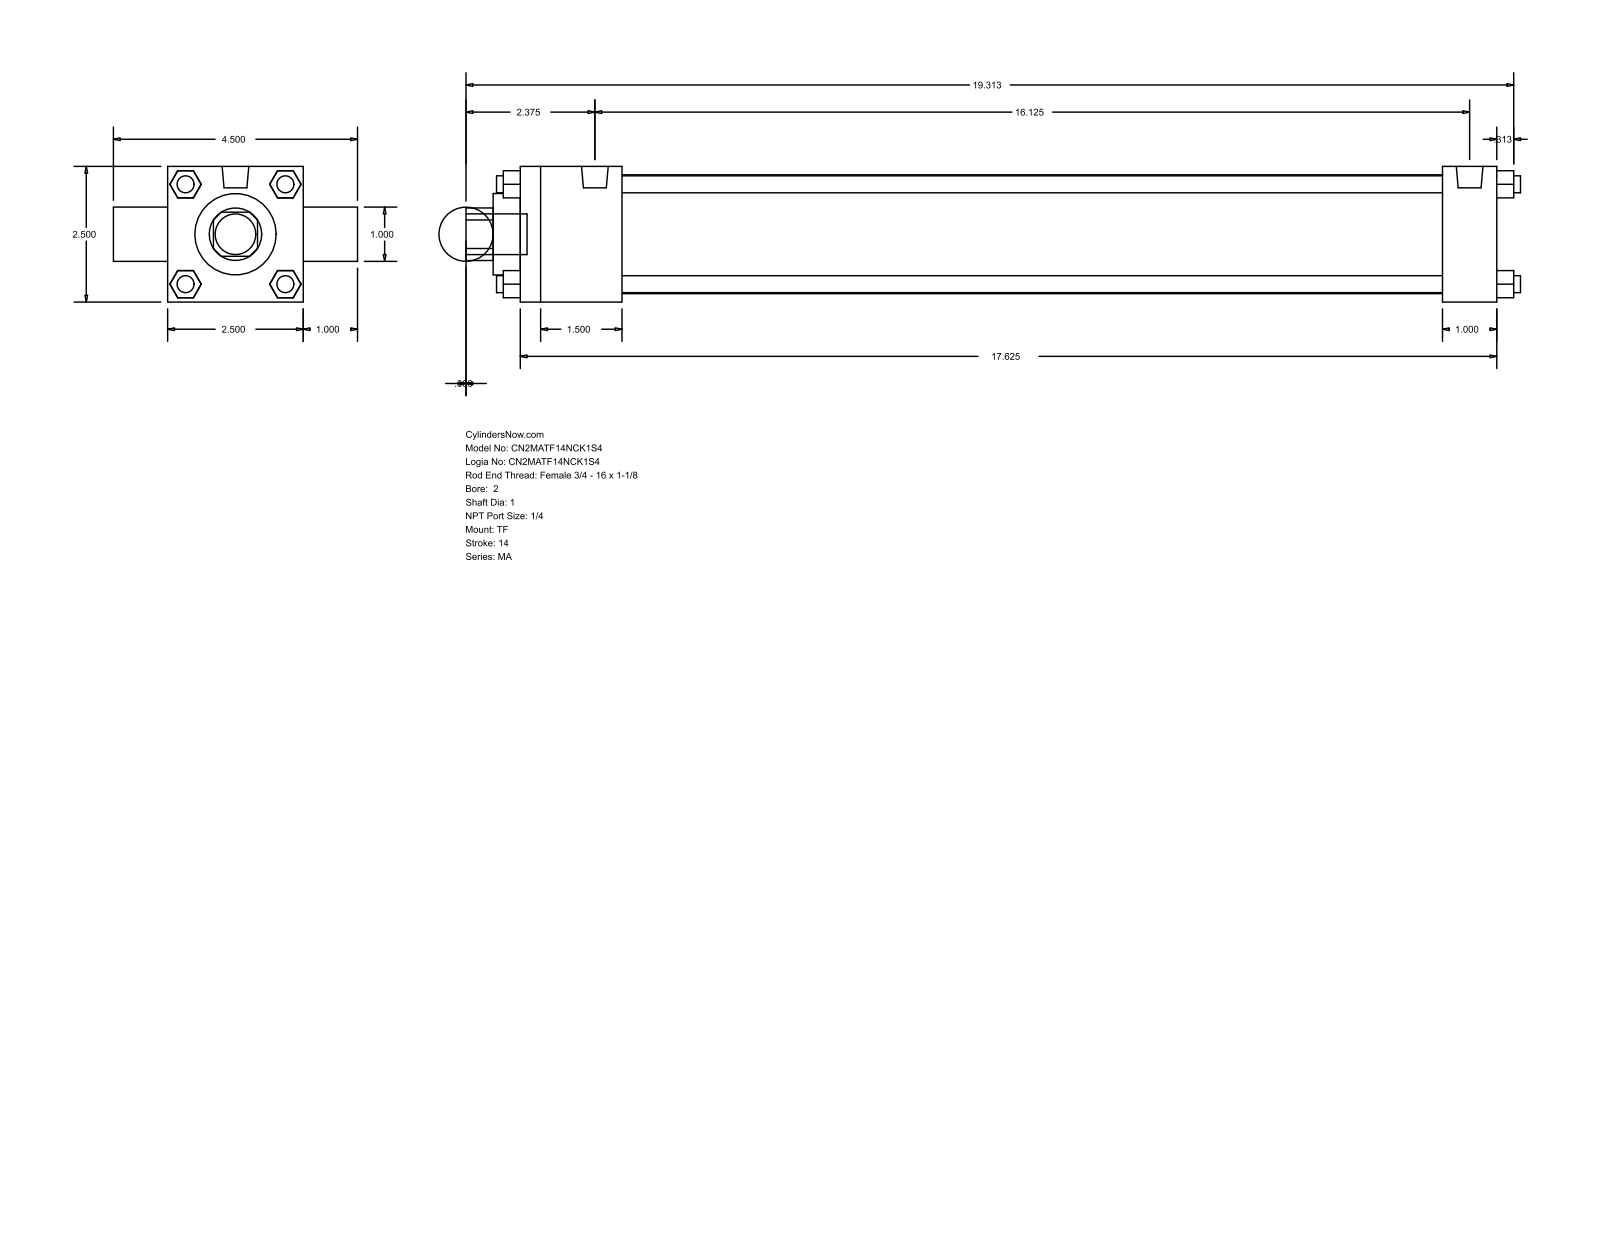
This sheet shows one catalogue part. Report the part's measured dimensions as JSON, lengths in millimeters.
{"part_name": "MA_TF__0200_1", "step_written_by": "GSSL Pune (CONFIG_CONTROL_DESIGN)", "units": "millimeters", "bodies": {"solids": 0, "faces": 120, "planar": 92, "cylindrical": 28, "other": 0}, "overall_size": [493.71, 114.3, 63.5], "round_holes": [[25.4, 2], [38.1, 1], [55.63, 1]], "round_bosses_or_shafts": [[7.94, 7], [12.49, 2], [19.05, 1]], "partial_cylinders_radius": [[12.29, 1]], "face_to_face_distances": [63.5, 25.4, 457.2, 12.7, 47.63, 431.8, 384.17, 409.57, 88.9, 23.37]}
